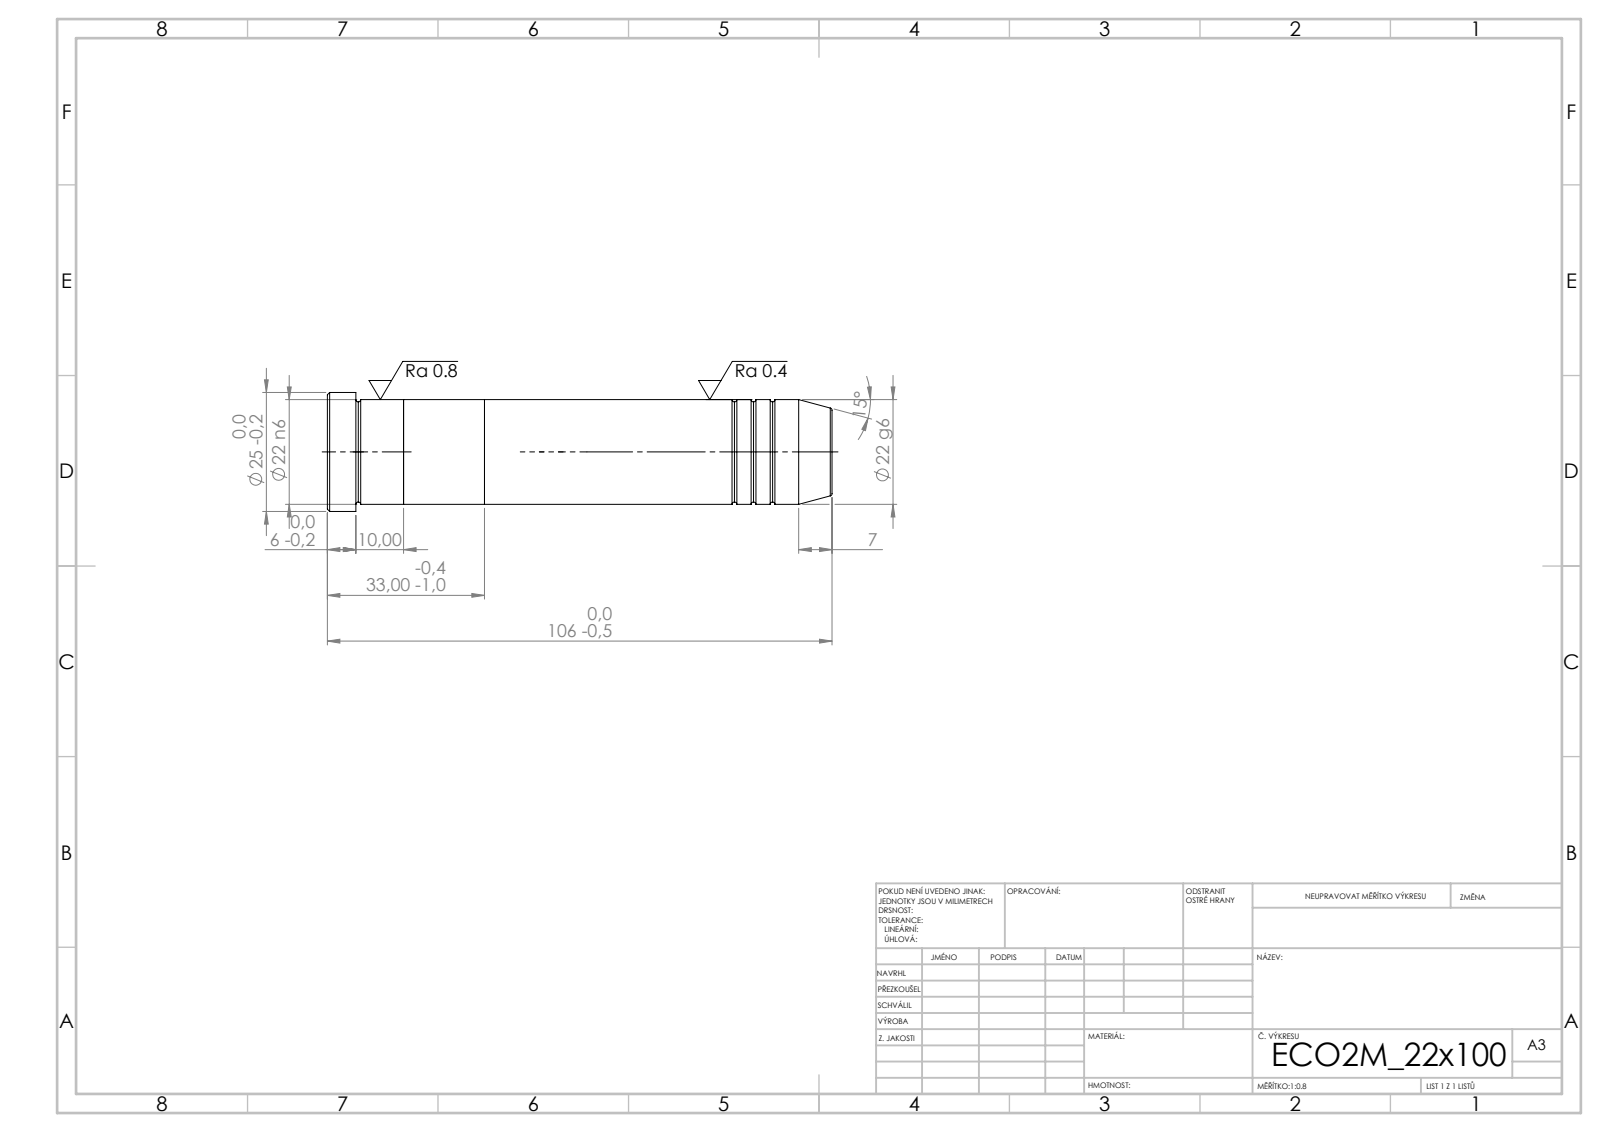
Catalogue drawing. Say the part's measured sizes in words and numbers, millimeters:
Its 3-D file was written by "SolidWorks 2019 (CONFIG_CONTROL_DESIGN)". It is 3 solids with 43 faces: 7 planar, 14 cylindrical and 22 other. Overall it measures 106 by 25 by 25 millimeters. Its volume is 40 413 cubic millimeters and its surface area 9 856 square millimeters. Round bosses or shafts: 1 of diameter 25, 1 of diameter 22. The main face-to-face distances are 17, 33, 16, 73, 90, 106, 100, 27, 10, 6.
